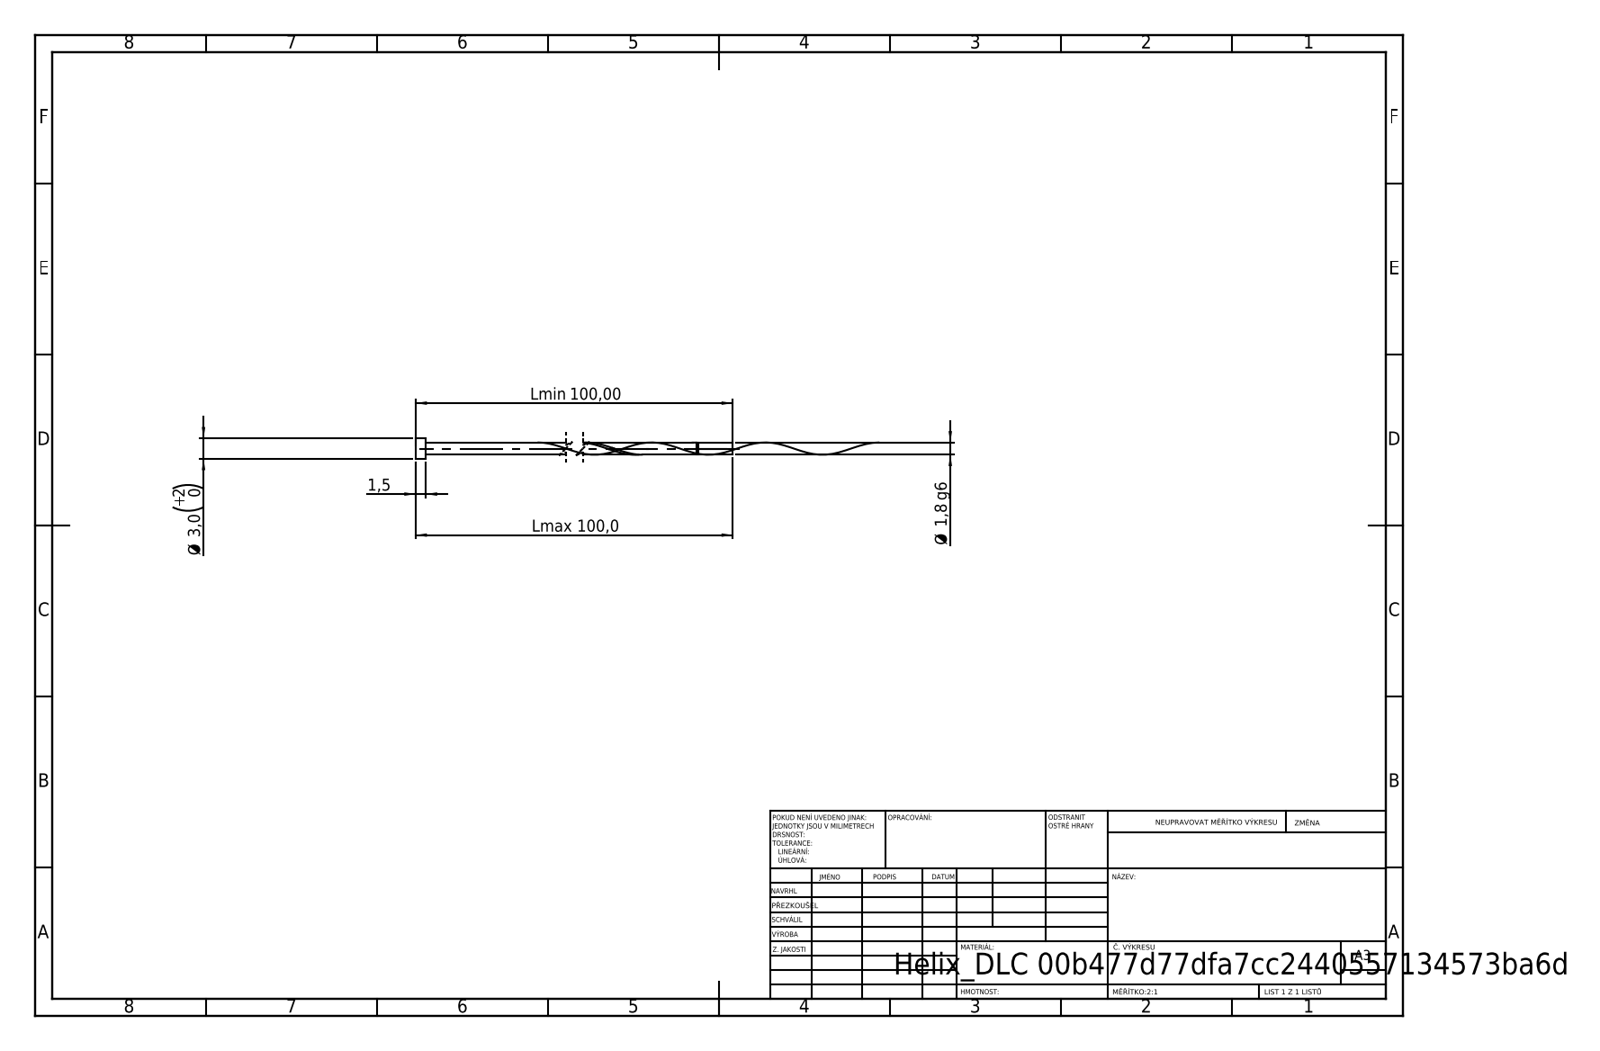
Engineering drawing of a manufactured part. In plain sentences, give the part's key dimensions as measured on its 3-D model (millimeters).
Its 3-D file was written by "SolidWorks 2019 (CONFIG_CONTROL_DESIGN)". It is 1 solid with 16 faces: 6 planar, 9 cylindrical and 1 other. Overall it measures 100 by 3 by 3 millimeters. Its volume is 315 cubic millimeters and its surface area 784 square millimeters. Round bosses or shafts: 1 of diameter 3, 1 of diameter 1.8, 1 of diameter 1.44. The main face-to-face distances are 1.5, 100, 98.5, 95, 93.5, 5, 94.64, 93.14, 0.36, 5.36.
